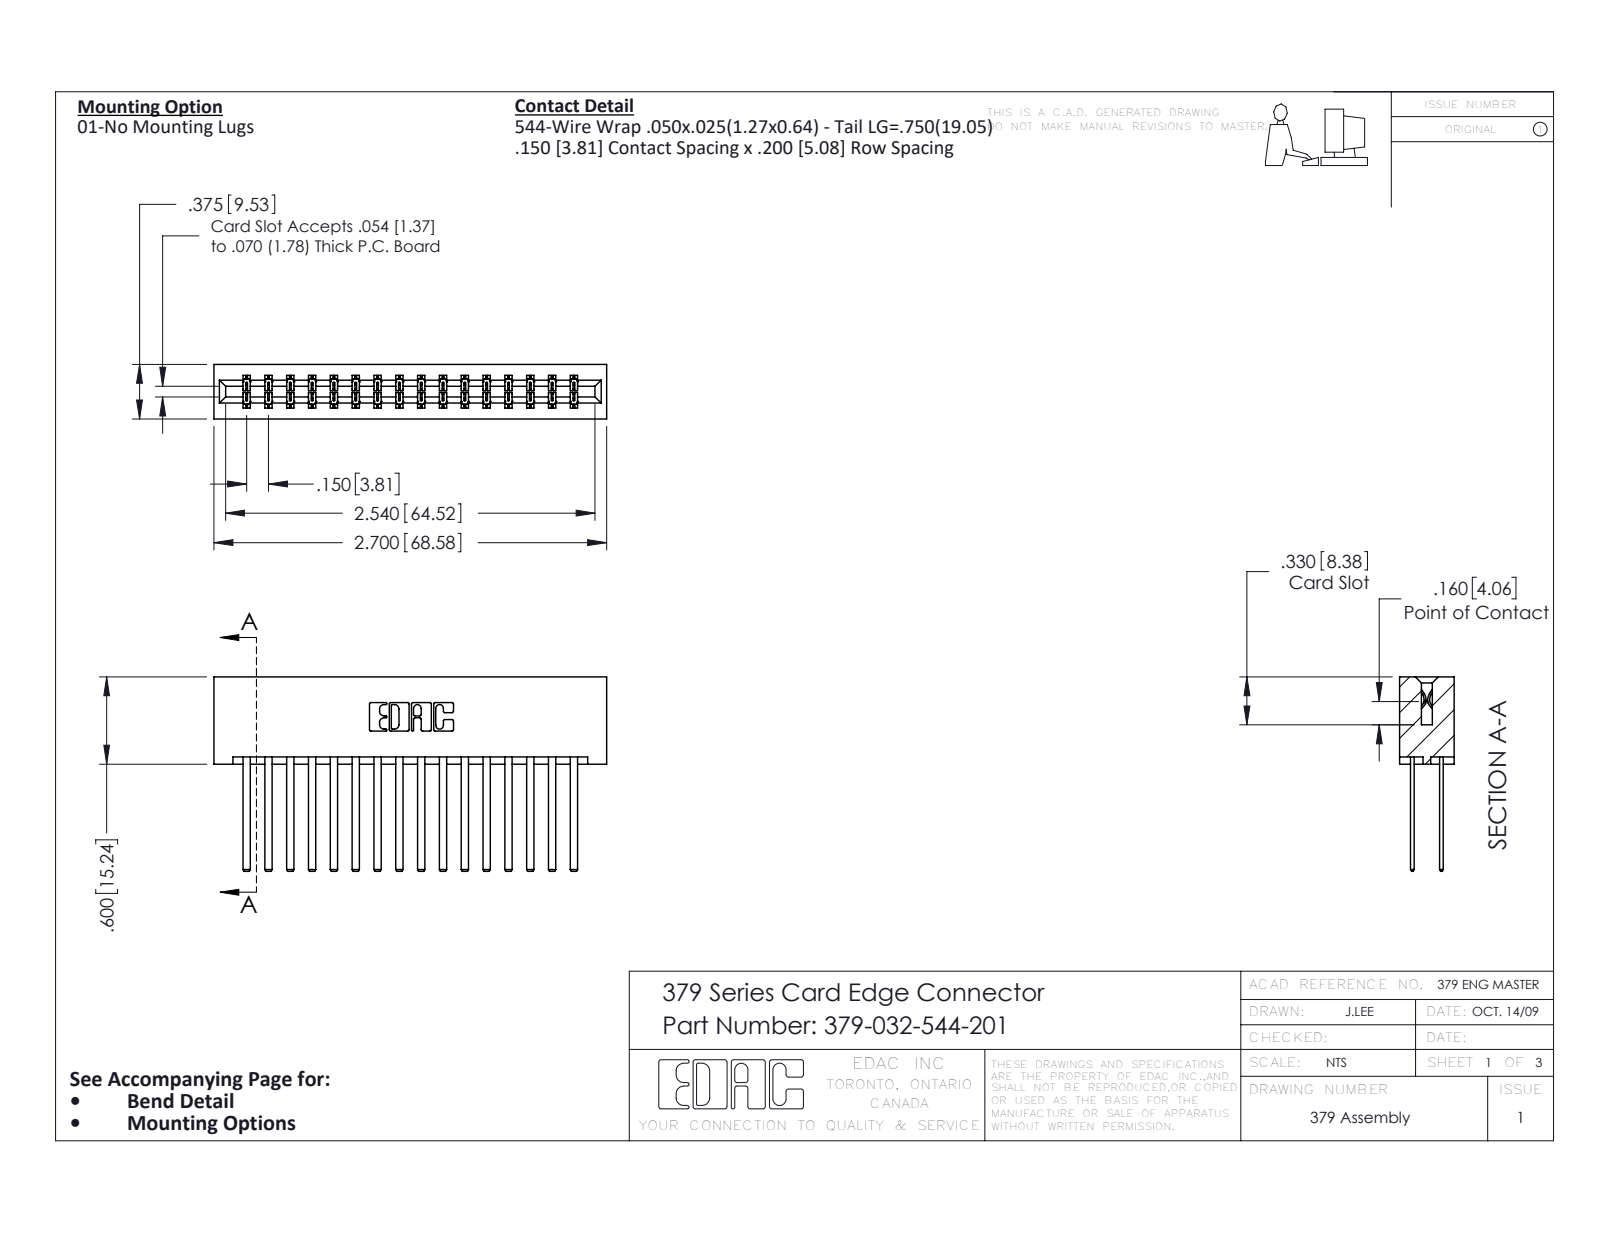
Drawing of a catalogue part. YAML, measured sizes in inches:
part_name: "379-032-544-201; 379 Part_Lugless; 345-292-001_345-293-144"
step_written_by: "SolidWorks 2020 (CONFIG_CONTROL_DESIGN)"
units: inches
bodies: {solids: 33, faces: 1578, planar: 1090, cylindrical: 488, other: 0}
overall_size: [2.7, 1.337, 0.375]
volume: 0.498
surface_area: 16.19
partial_cylinders:
  - {radius: 0.006, count: 48}
  - {radius: 0.01, count: 22}
  - {radius: 0.007, count: 6}
  - {radius: 0.031, count: 6}
  - {radius: 0.026, count: 3}
  - {radius: 0.014, count: 2}
  - {radius: 0.022, count: 2}
  - {radius: 0.024, count: 2}
face_to_face_distances: [0.3, 0.075, 0.2, 0.1, 0.15, 0.275, 0.025, 0.225, 0.375, 0.45]
